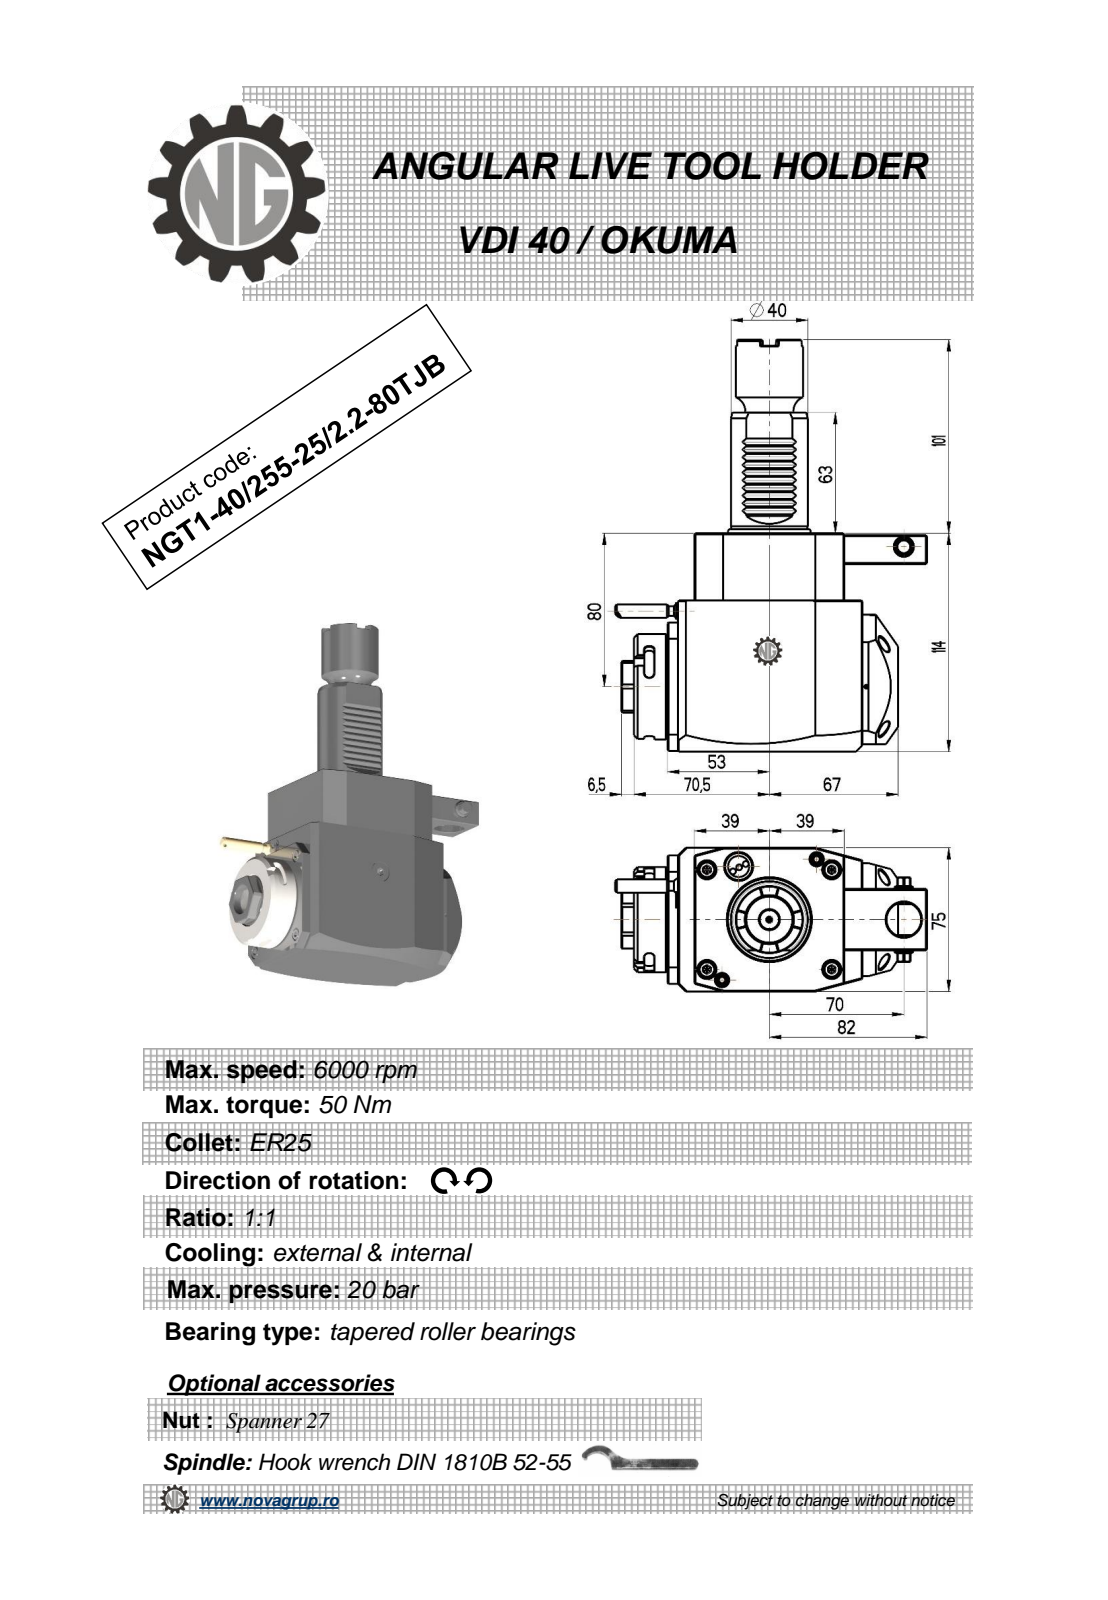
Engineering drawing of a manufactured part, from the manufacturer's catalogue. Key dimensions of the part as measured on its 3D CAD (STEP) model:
Part name (STEP PRODUCT): NGT1_40_255_25_1_2_80TJB
STEP written by: PRO/ENGINEER BY PARAMETRIC TECHNOLOGY CORPORATION, 2010280 (CONFIG_CONTROL_DESIGN)
Units: millimetres
Bodies: 1 solid, 384 faces (196 planar, 82 cylindrical, 106 other)
Overall size (bounding box): 215 × 162.33 × 75
Volume: 994 268 mm³ · Surface area: 77 070 mm²
Round holes (diameter × count): ⌀18 ×2, ⌀2.5 ×1, ⌀3 ×1, ⌀9.5 ×1, ⌀25 ×1
Round bosses / shafts (diameter × count): ⌀8.96 ×2, ⌀55 ×1, ⌀48 ×1, ⌀40 ×1, ⌀35 ×1, ⌀10 ×1, ⌀7 ×1, ⌀5 ×1
Partial cylindrical surfaces — rounded edges, fillets, slot ends (radius × count): R0.3 ×10, R2.5 ×6, R180 ×2, R0.5 ×1, R3.85 ×1, R4.25 ×1, R15 ×1, R24.5 ×1
Main face-to-face distances: 75, 114, 14, 17.5, 109.5, 79, 92, 78, 31.5, 98
Hole centre spacings: 37.35, 43.2, 70, 72.5
